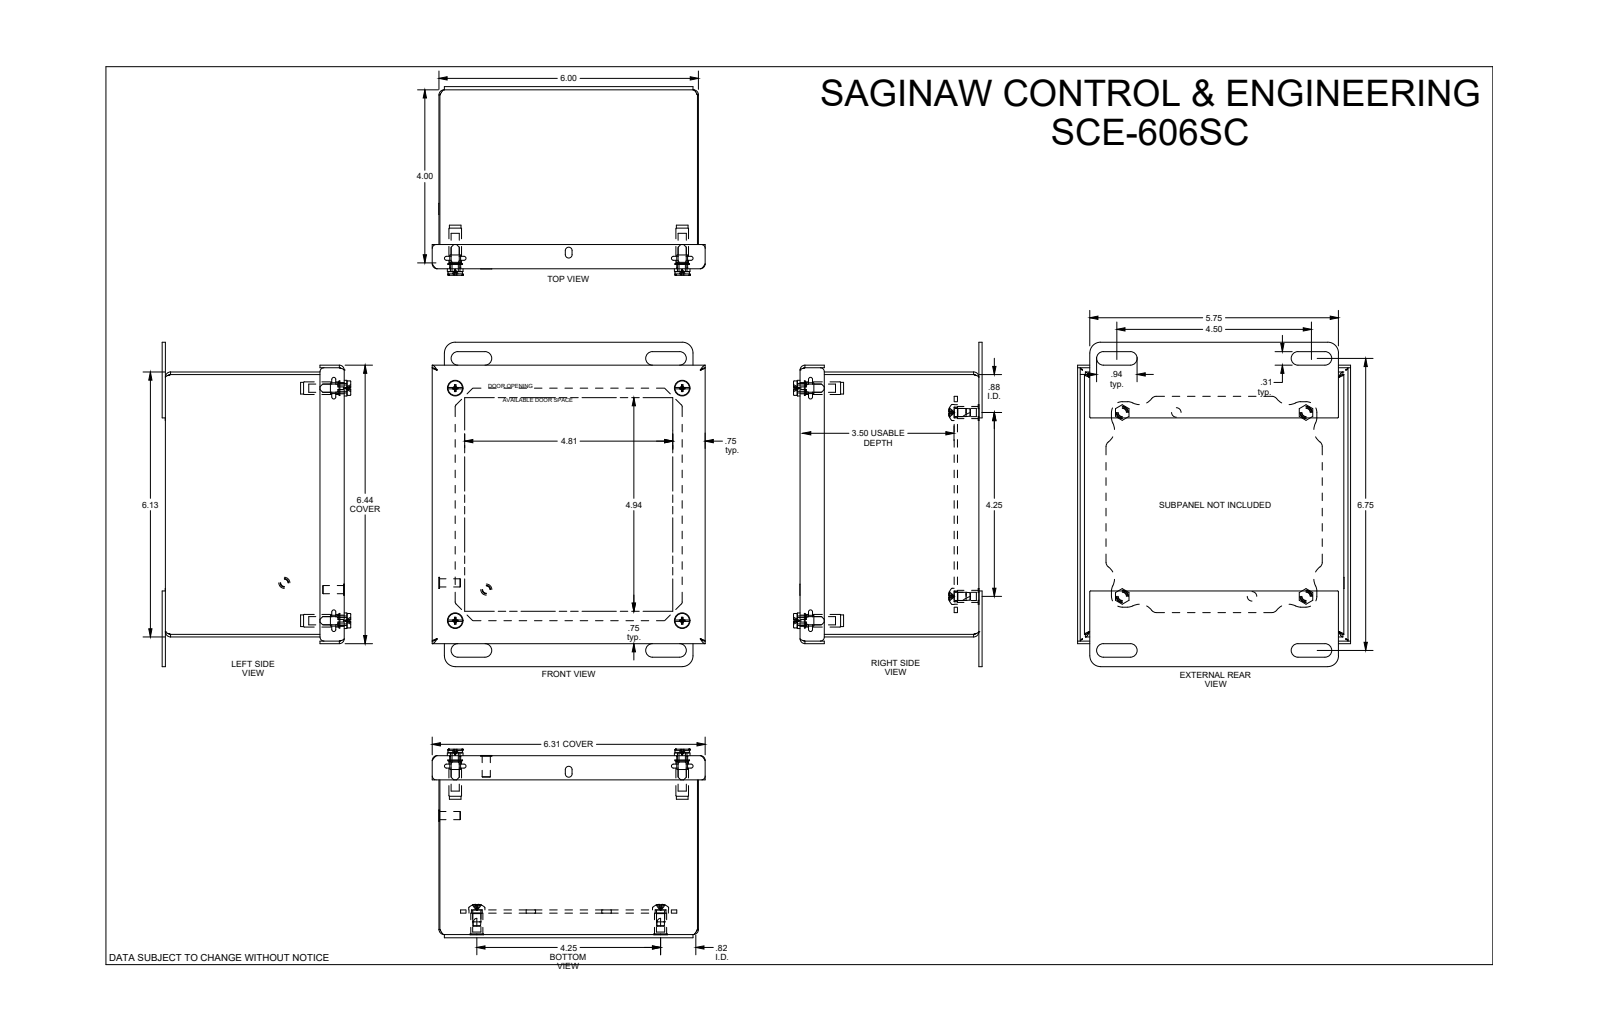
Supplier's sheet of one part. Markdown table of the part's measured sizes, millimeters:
| quantity | value |
| --- | --- |
| part name | SCE-606SC |
| STEP written by | SolidWorks 2019 (CONFIG_CONTROL_DESIGN) |
| units | millimeters |
| bodies | 0 solids, 879 faces (397 planar, 216 cylindrical, 266 other) |
| overall size | 190.5 × 160.4 × 110.8 |
| round holes (diameter × count) | 4.8 × 8, 6.4 × 8, 5.6 × 4, 6.8 × 4, 7.1 × 4, 8.1 × 4, 4.9 × 2, 5.5 × 2 |
| round bosses / shafts (diameter × count) | 4.8 × 10, 9.5 × 4, 9.2 × 4, 8.6 × 4, 8.5 × 4, 7.4 × 4, 7.1 × 4, 6.9 × 4 |
| partial cylindrical surfaces (radius × count) | 3.2 × 16, 6.4 × 16, 0.1 × 8, 0.2 × 8, 1.3 × 8, 2.8 × 8, 4 × 8, 6.5 × 8 |
| main face-to-face distances | 1.5, 103.5, 1.5, 150.9, 154.1, 102, 105, 103.5, 3.4, 1.9 |
| hole center spacings | 122.9, 136.5, 19.1, 108, 171.8, 190.9, 130.1, 19.1 |
